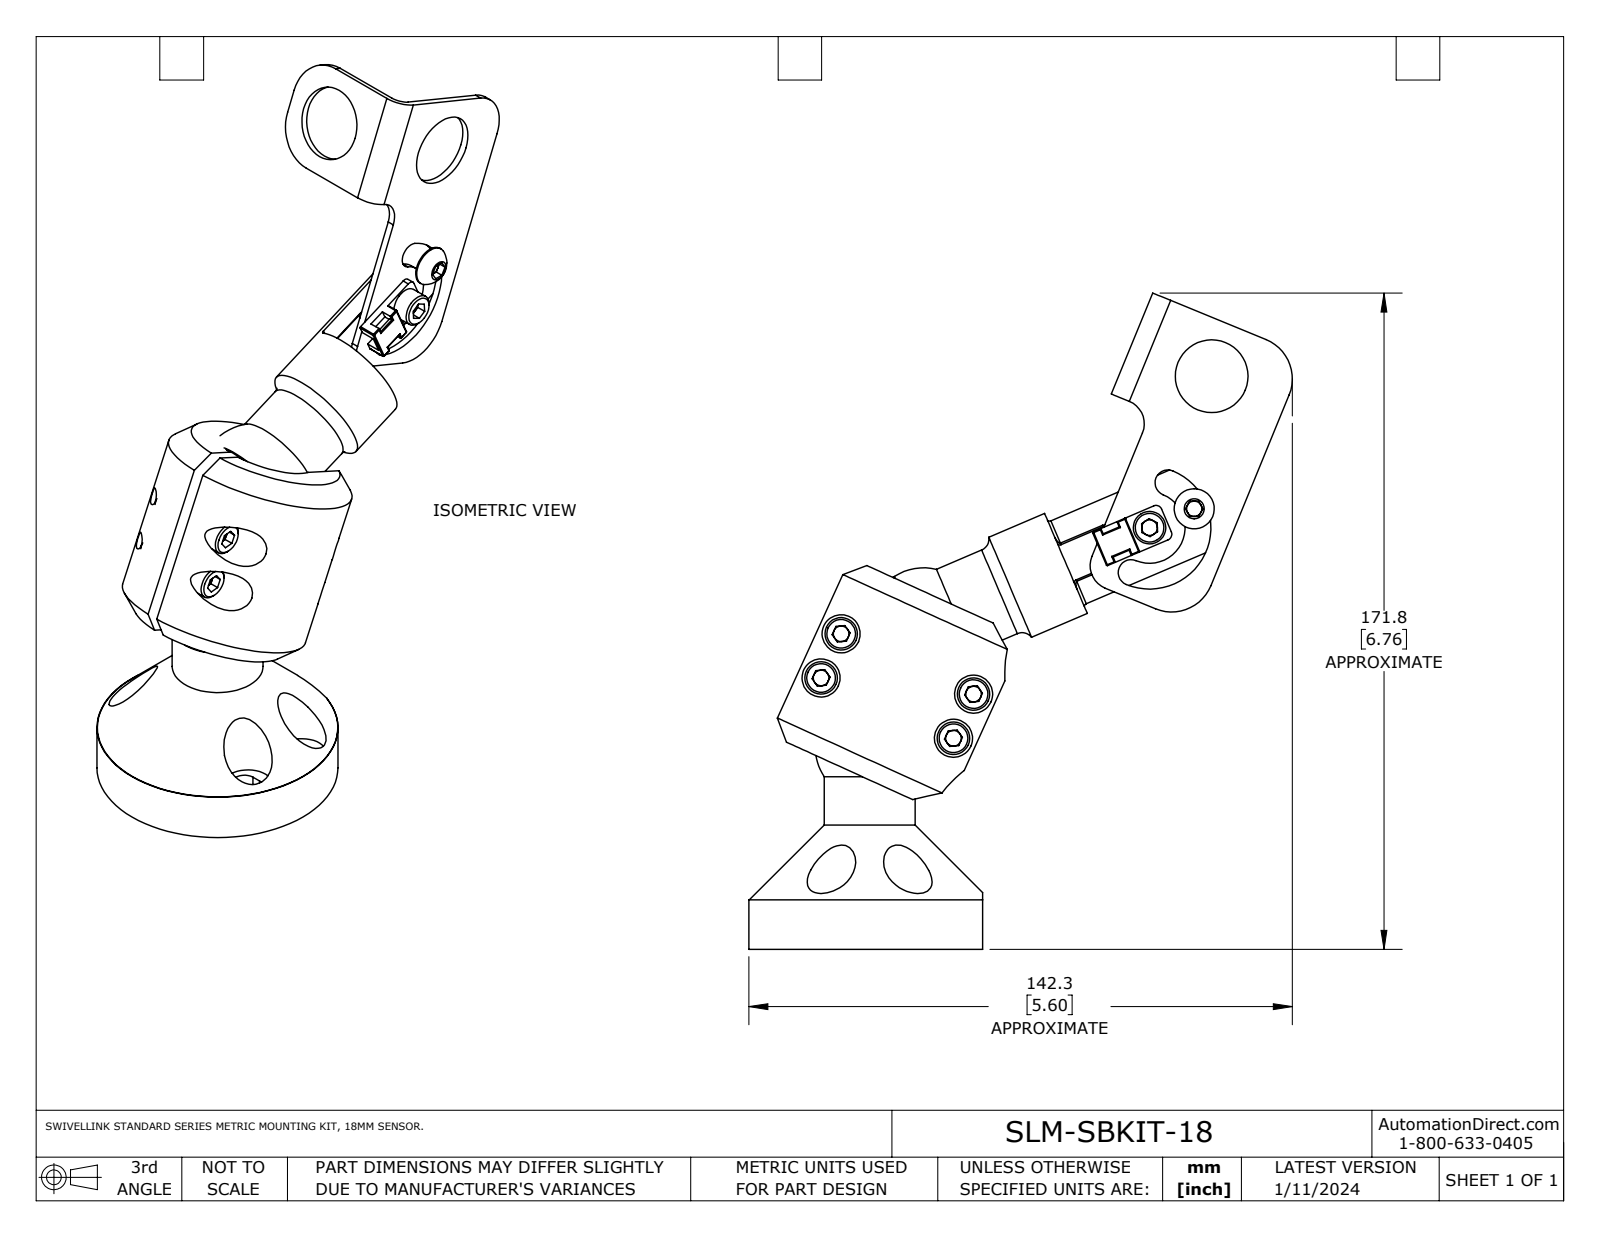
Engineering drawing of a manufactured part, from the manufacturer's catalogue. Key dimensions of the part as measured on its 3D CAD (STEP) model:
Part name (STEP PRODUCT): SLM-SBKIT-18
STEP written by: SolidWorks 2023 (AUTOMOTIVE_DESIGN)
Units: inches
Bodies: 12 solids, 311 faces (160 planar, 93 cylindrical, 58 other)
Overall size (bounding box): 6.764 × 5.604 × 2.881
Volume: 8.333 in³ · Surface area: 83.59 in²
Round holes (diameter × count): ⌀0.165 ×5, ⌀0.228 ×4, ⌀0.394 ×4, ⌀0.5 ×4, ⌀0.75 ×3, ⌀0.197 ×1, ⌀0.2 ×1, ⌀0.281 ×1, ⌀0.813 ×1, ⌀1 ×1
Round bosses / shafts (diameter × count): ⌀0.335 ×5, ⌀0.197 ×5, ⌀0.937 ×2, ⌀2.485 ×1, ⌀1.98 ×1, ⌀1.122 ×1, ⌀0.413 ×1, ⌀0.236 ×1
Partial cylindrical surfaces — rounded edges, fillets, slot ends (radius × count): R0.01 ×12, R0.121 ×8, R0.437 ×4, R0.375 ×3, R0.063 ×2, R0.133 ×2, R0.25 ×2, R0.497 ×2
Main face-to-face distances: 0.075, 0.189, 0.264, 0.125, 0.314, 0.389, 2, 0.074, 0.187, 0.312
Hole centre spacings: 0.925, 0.5, 0.787, 1.5, 1.581, 1.673, 1.849, 1.378
